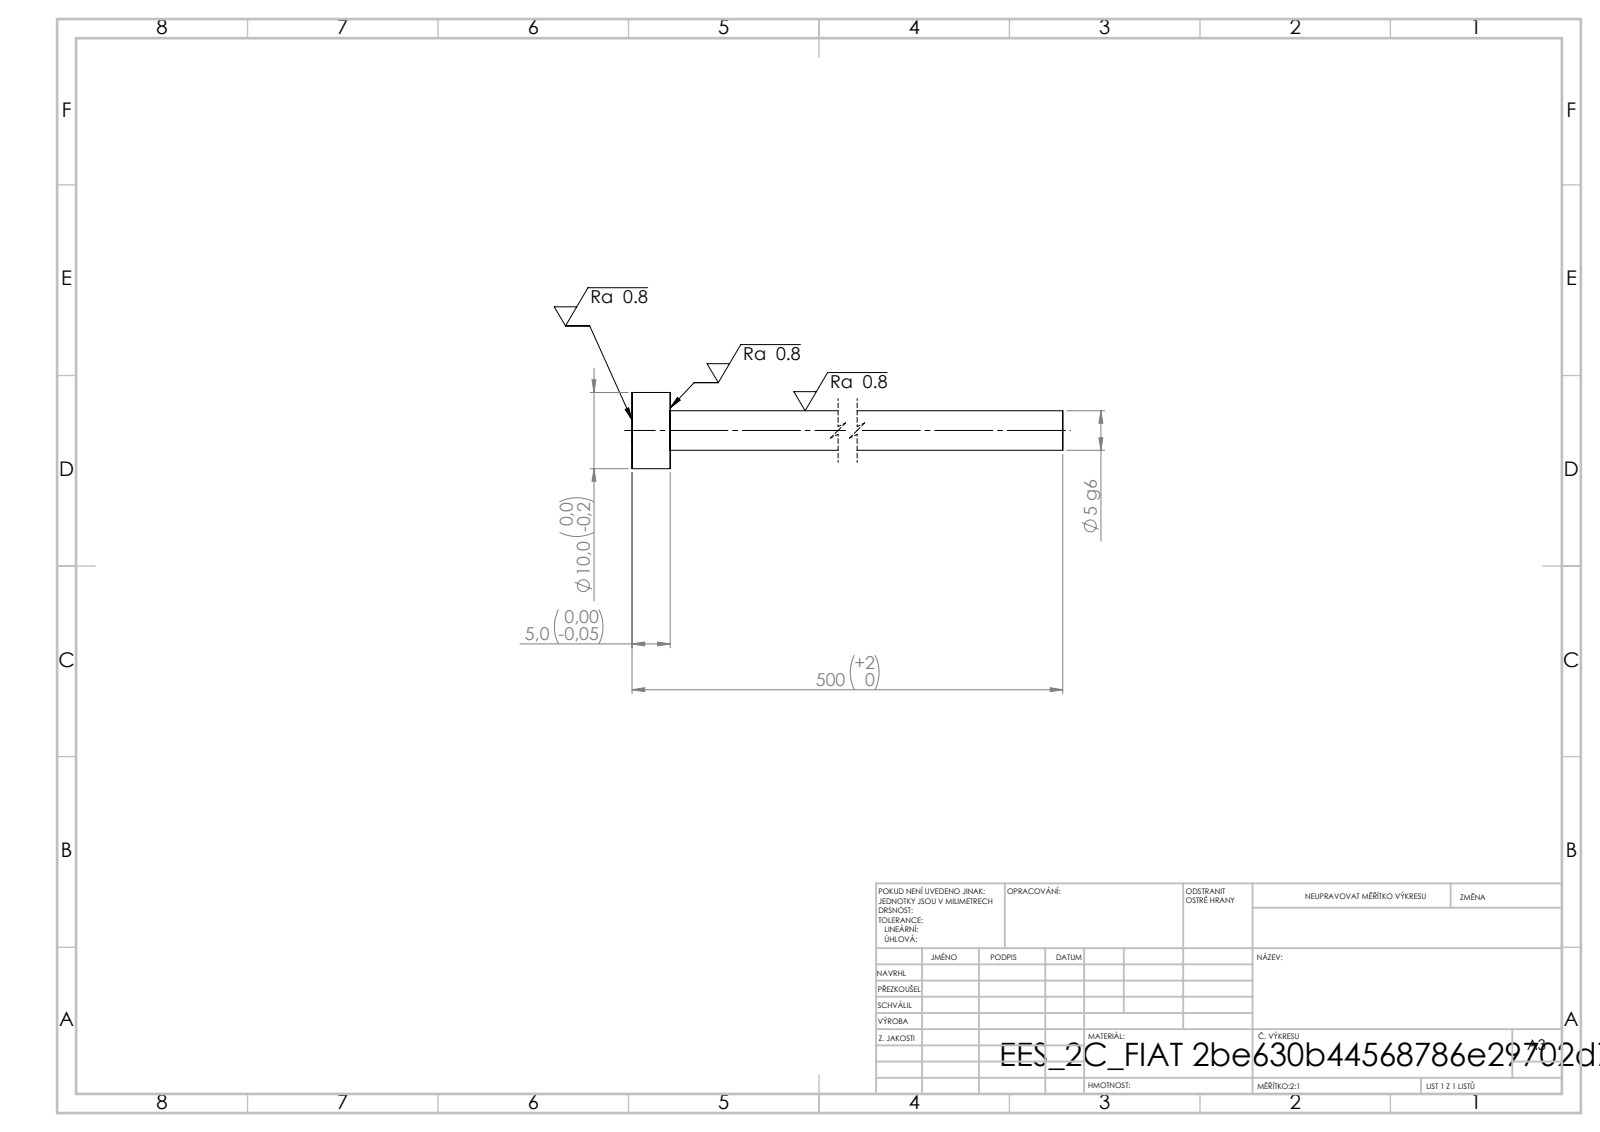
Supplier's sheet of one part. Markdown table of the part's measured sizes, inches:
| quantity | value |
| --- | --- |
| STEP written by | SolidWorks 2019 (CONFIG_CONTROL_DESIGN) |
| units | inches |
| bodies | 1 solid, 7 faces (3 planar, 4 cylindrical, 0 other) |
| overall size | 19.685 × 0.394 × 0.394 |
| volume | 0.665 in³ |
| surface area | 13.02 in² |
| round bosses / shafts (diameter × count) | 0.394 × 1, 0.205 × 1 |
| main face-to-face distances | 0.197, 19.685, 19.488 |
